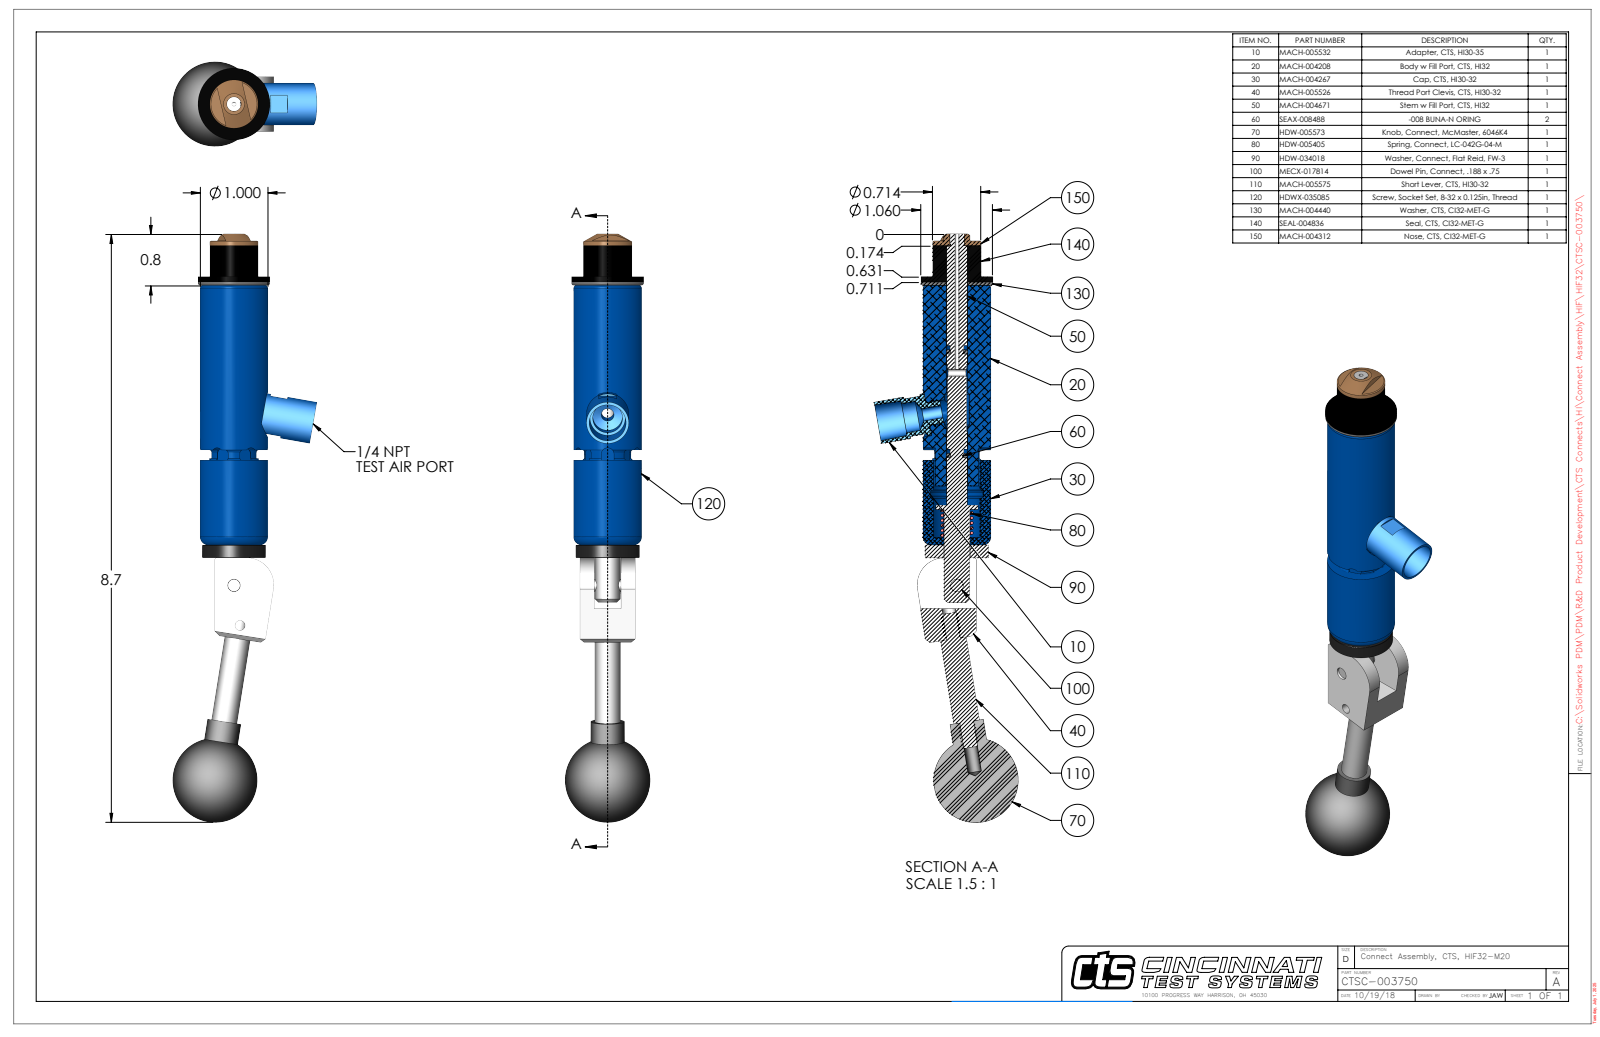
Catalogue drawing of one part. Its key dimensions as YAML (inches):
part_name: "CTSC-003750"
step_written_by: "SolidWorks 2023 (AUTOMOTIVE_DESIGN)"
units: inches
bodies: {solids: 9, faces: 297, planar: 112, cylindrical: 120, other: 65}
overall_size: [8.704, 2.128, 1.25]
volume: 5.246
surface_area: 41.98
round_holes:
  - {diameter: 0.201, count: 2}
  - {diameter: 0.063, count: 1}
  - {diameter: 0.109, count: 1}
  - {diameter: 0.136, count: 1}
  - {diameter: 0.15, count: 1}
  - {diameter: 0.187, count: 1}
  - {diameter: 0.189, count: 1}
  - {diameter: 0.213, count: 1}
  - {diameter: 0.31, count: 1}
  - {diameter: 0.314, count: 1}
  - {diameter: 0.316, count: 1}
  - {diameter: 0.385, count: 1}
round_bosses_or_shafts:
  - {diameter: 0.25, count: 2}
  - {diameter: 0.201, count: 2}
  - {diameter: 1.06, count: 1}
  - {diameter: 1, count: 1}
  - {diameter: 0.936, count: 1}
  - {diameter: 0.714, count: 1}
  - {diameter: 0.62, count: 1}
  - {diameter: 0.5, count: 1}
partial_cylinders:
  - {radius: 0.093, count: 6}
  - {radius: 0.029, count: 2}
  - {radius: 0.058, count: 1}
  - {radius: 0.325, count: 1}
  - {radius: 0.375, count: 1}
  - {radius: 0.4, count: 1}
  - {radius: 0.473, count: 1}
face_to_face_distances: [0.05, 0.21, 0.602, 3.883, 3.833, 0.812, 0.537, 0.587, 4.42, 4.608]
hole_center_spacings: [0.599, 1.658, 2.252]
